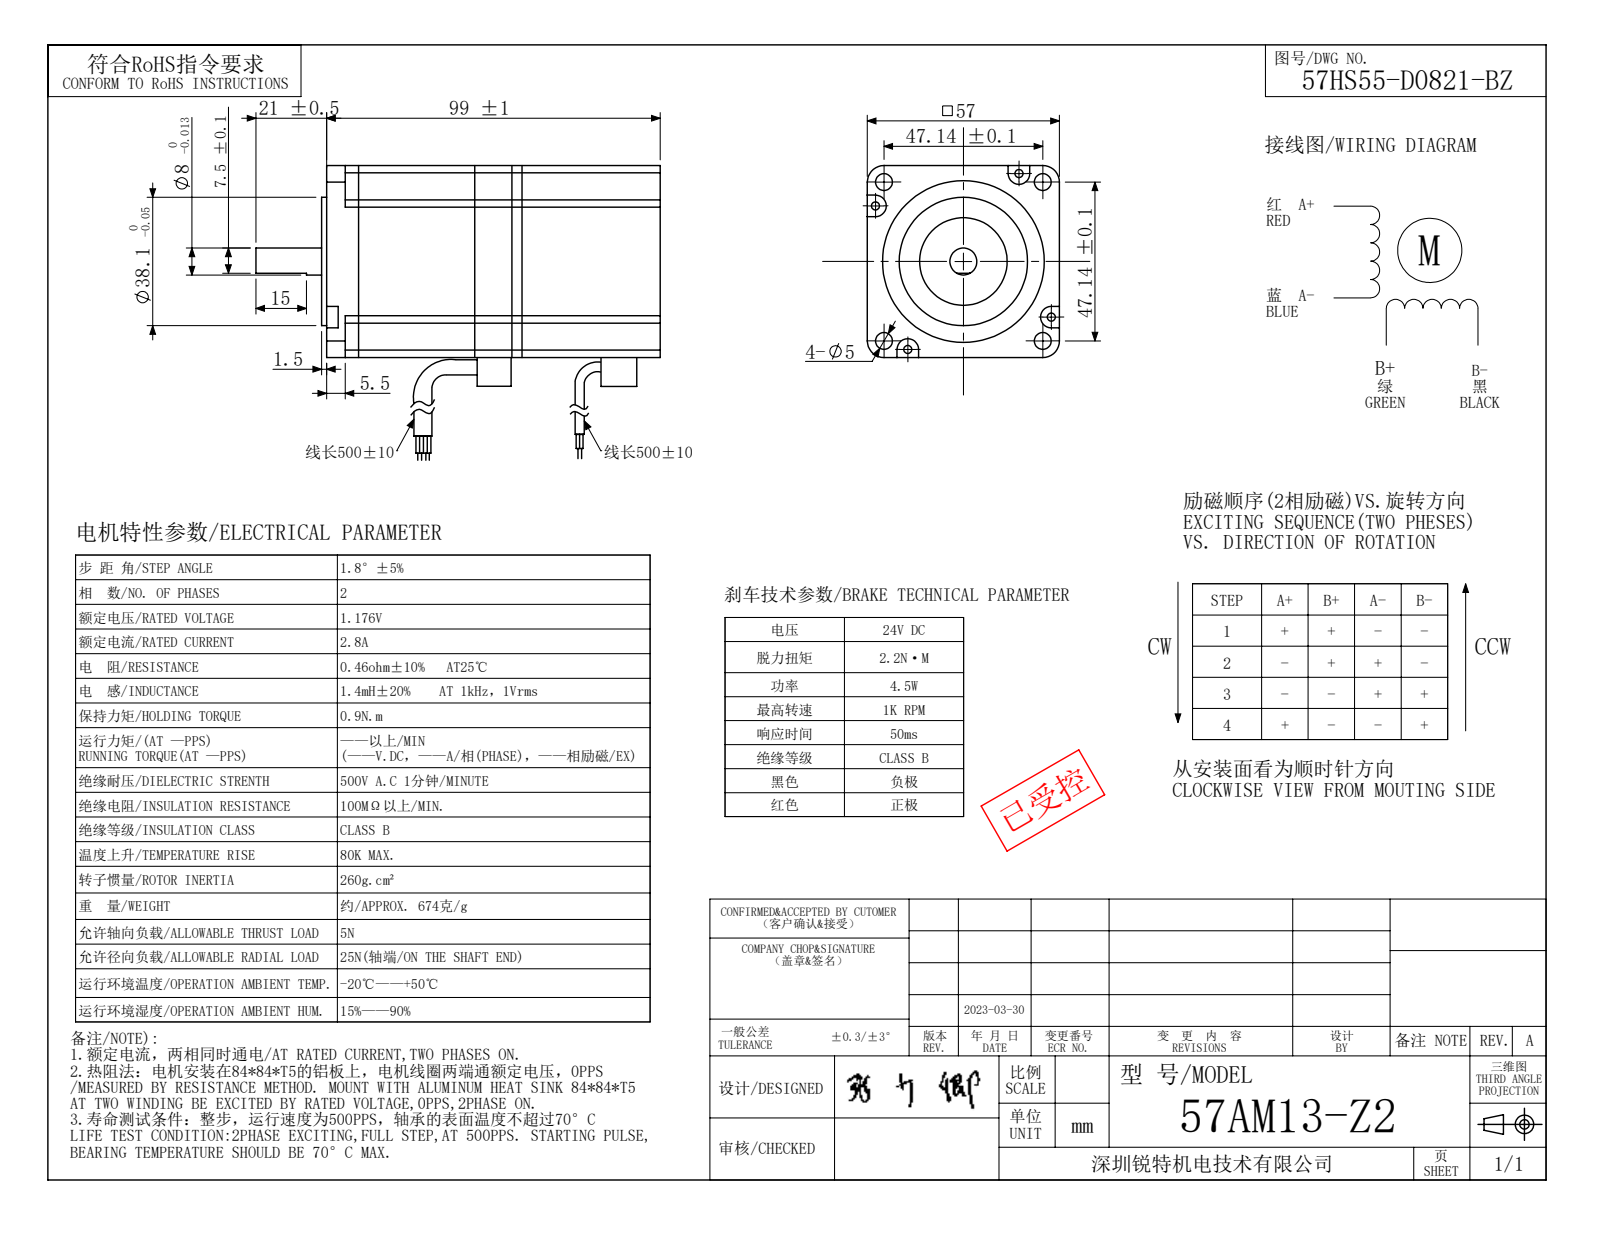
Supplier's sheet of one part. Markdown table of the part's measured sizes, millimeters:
| quantity | value |
| --- | --- |
| STEP written by | SolidWorks 2020 (AUTOMOTIVE_DESIGN) |
| units | millimeters |
| bodies | 1 solid, 77 faces (32 planar, 45 cylindrical, 0 other) |
| overall size | 120 × 57 × 57 |
| volume | 286 078 mm³ |
| surface area | 31 025 mm² |
| round holes (diameter × count) | 2.4 × 4, 5 × 4, 26 × 1, 48 × 1 |
| round bosses / shafts (diameter × count) | 38.1 × 1, 8 × 1 |
| partial cylindrical surfaces (radius × count) | 2.2 × 8, 3.2 × 4, 4.93 × 4, 8 × 4 |
| main face-to-face distances | 57, 99, 98.25, 0.75, 100.5, 2.25, 1.5, 99.3, 1.05, 1.2 |
| hole center spacings | 7.51, 30.88, 33.33, 40.15, 43.67, 47.14, 50.17, 63.82 |
